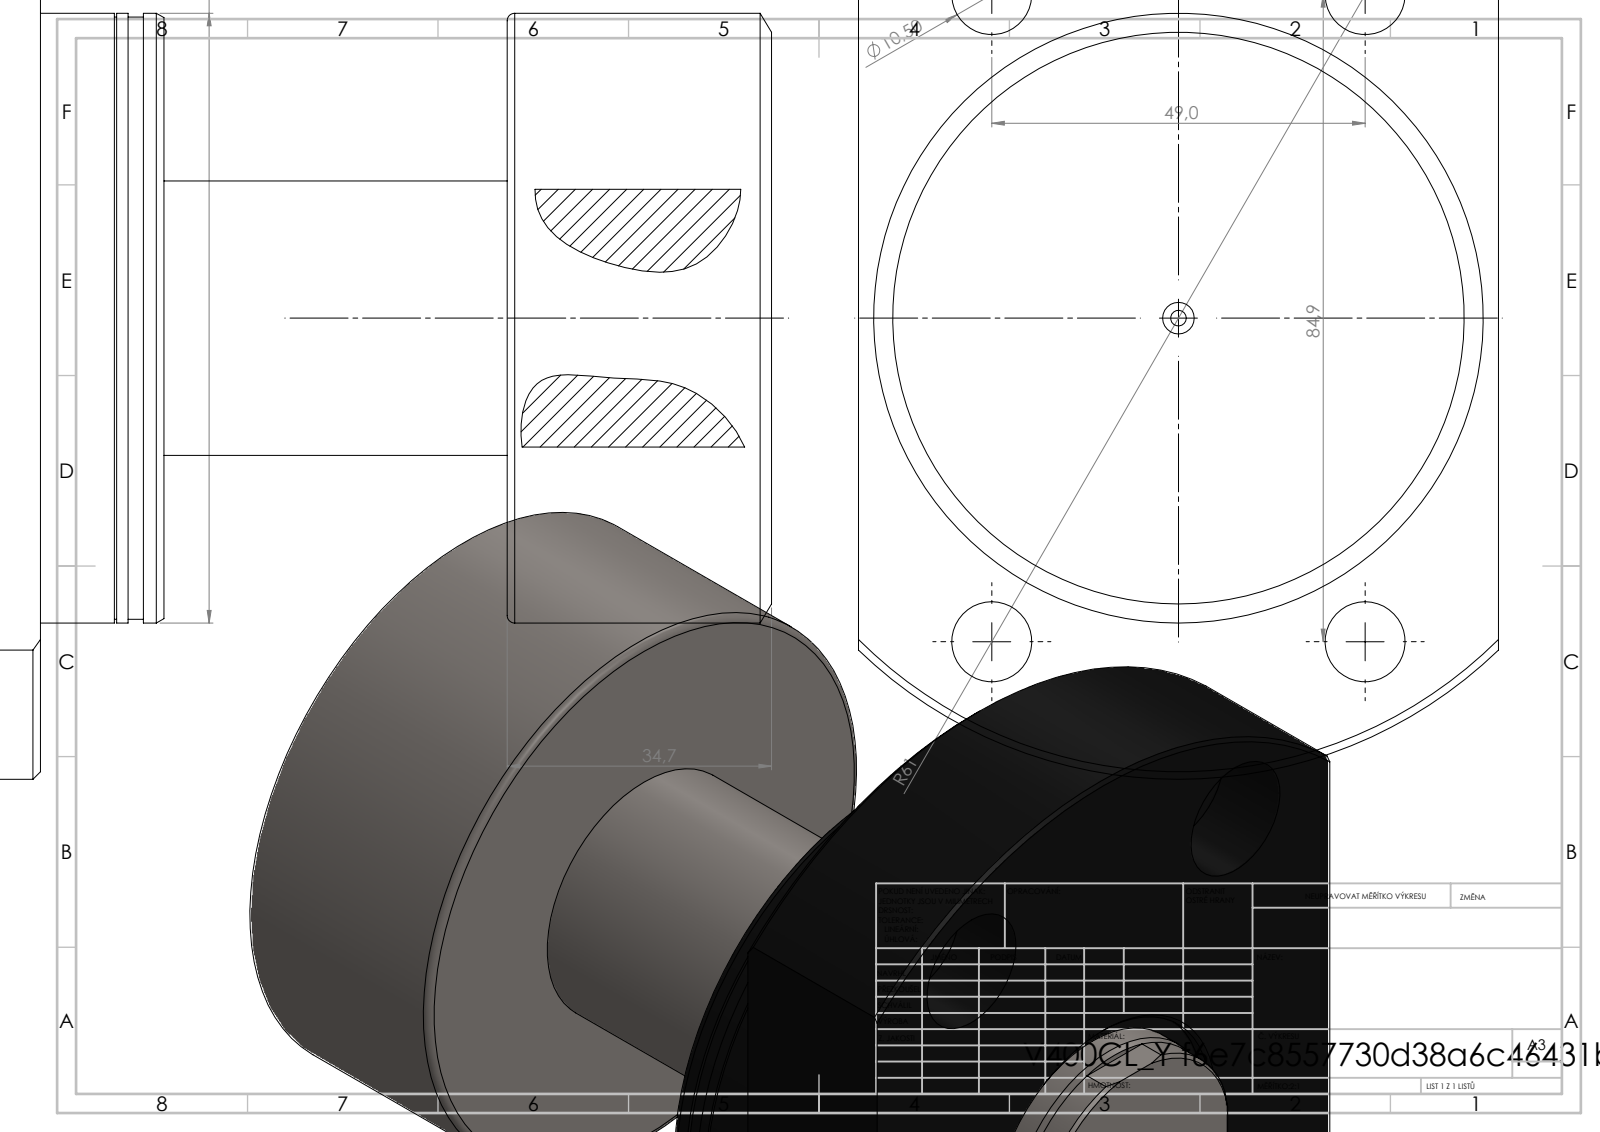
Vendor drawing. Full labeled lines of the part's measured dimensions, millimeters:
Part name (STEP PRODUCT): V400CL_PC_Y; V400CL_VC_X
STEP written by: SolidWorks 2019 (CONFIG_CONTROL_DESIGN)
Units: millimetres
Bodies: 2 solids, 103 faces (26 planar, 47 cylindrical, 30 other)
Overall size (bounding box): 126 × 121 × 84
Volume: 514 413 mm³ · Surface area: 66 243 mm²
Round holes (diameter × count): ⌀10.5 ×4, ⌀16.5 ×4, ⌀2.05 ×1, ⌀5 ×1, ⌀6 ×1, ⌀36 ×1, ⌀40.5 ×1
Round bosses / shafts (diameter × count): ⌀80 ×1, ⌀79 ×1
Partial cylindrical surfaces — rounded edges, fillets, slot ends (radius × count): R17.75 ×1, R60.5 ×1
Main face-to-face distances: 119.95, 34.7, 85.25, 79.75, 45.05, 40.2, 95.95, 61.25, 16.2, 24
Hole centre spacings: 49.01, 49, 84.9, 98.03
